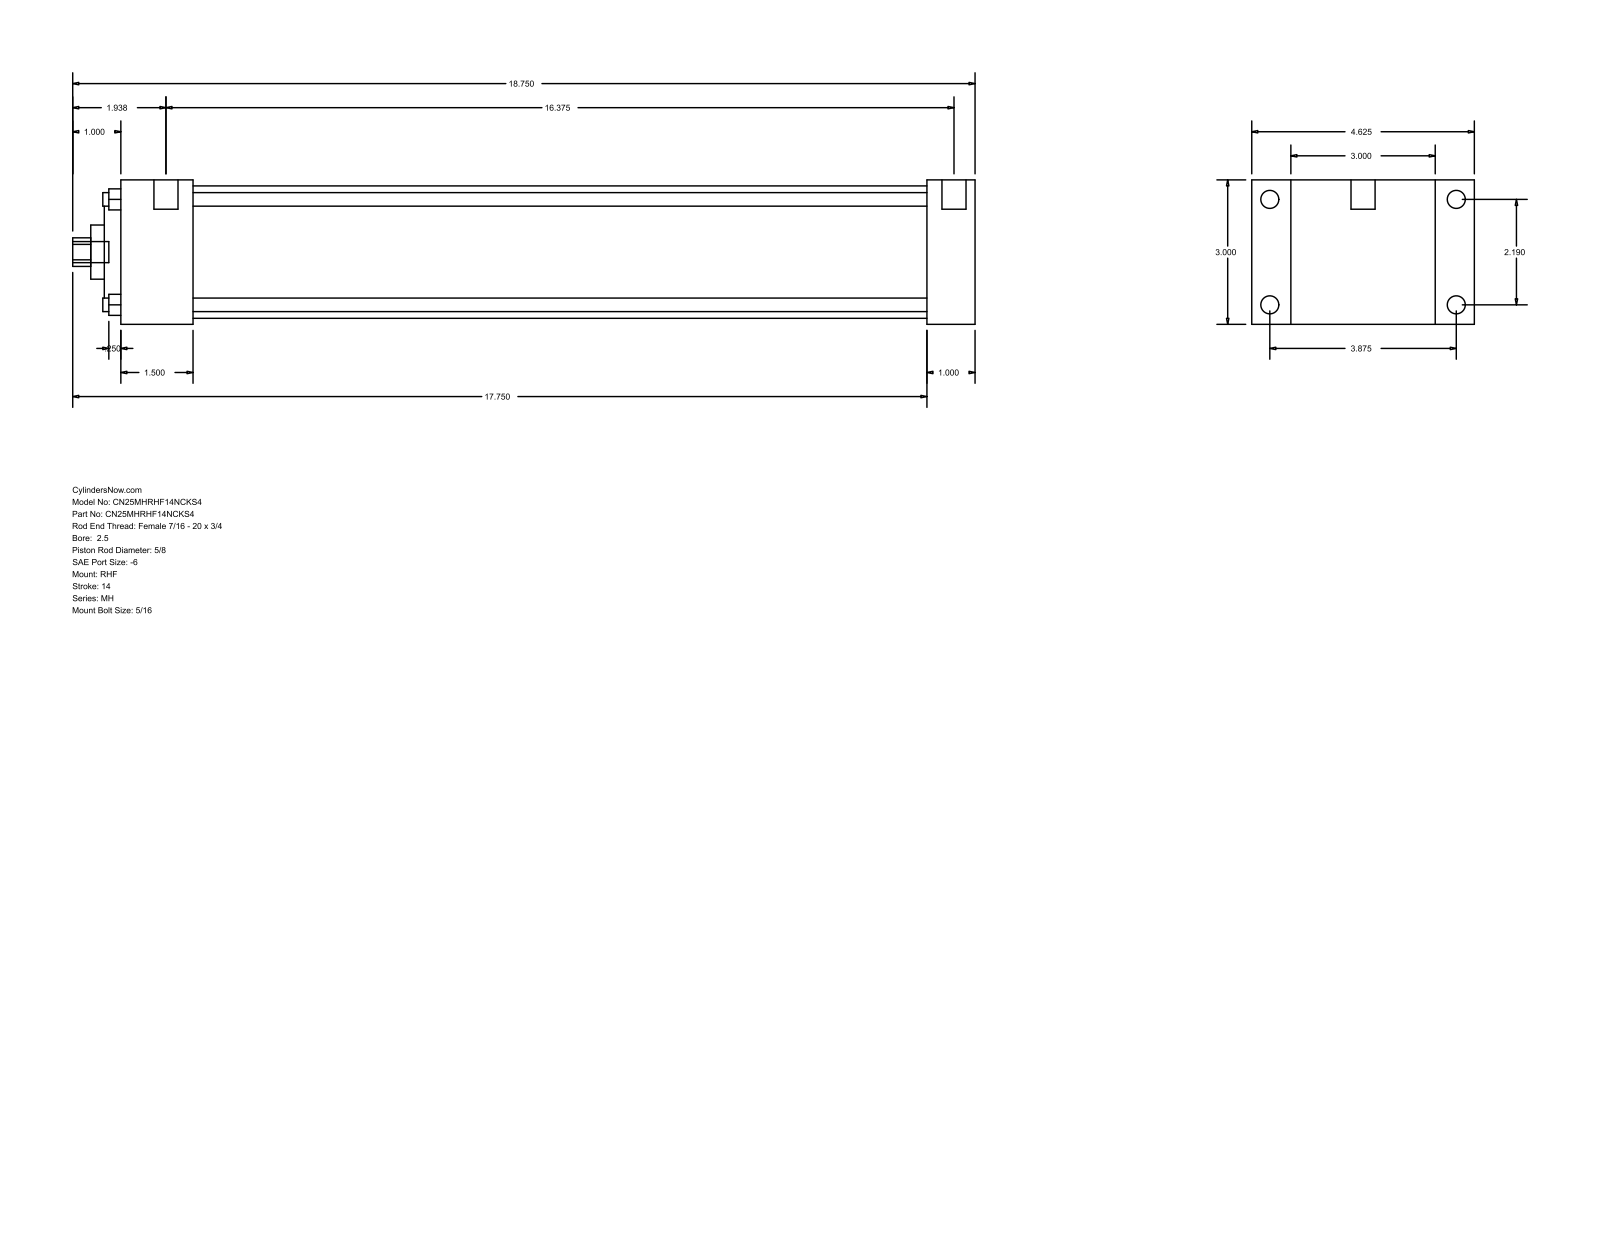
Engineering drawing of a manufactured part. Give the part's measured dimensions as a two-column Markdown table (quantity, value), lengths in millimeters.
| quantity | value |
| --- | --- |
| part name | MH_RHF__0250_0.625 |
| STEP written by | GSSL Pune (CONFIG_CONTROL_DESIGN) |
| units | millimeters |
| bodies | 0 solids, 90 faces (61 planar, 29 cylindrical, 0 other) |
| overall size | 476.25 × 117.47 × 76.2 |
| round holes (diameter × count) | 7.14 × 4, 15.88 × 1, 28.57 × 1, 55.55 × 1, 69.85 × 1 |
| round bosses / shafts (diameter × count) | 9.53 × 4, 5.56 × 4, 12.7 × 2, 11.11 × 1 |
| partial cylindrical surfaces (radius × count) | 7.54 × 1 |
| main face-to-face distances | 76.2, 25.4, 20.64, 96.84, 450.85, 425.45, 117.48, 38.1, 387.35, 412.75 |
| hole center spacings | 39.33, 55.62, 78.66 |
